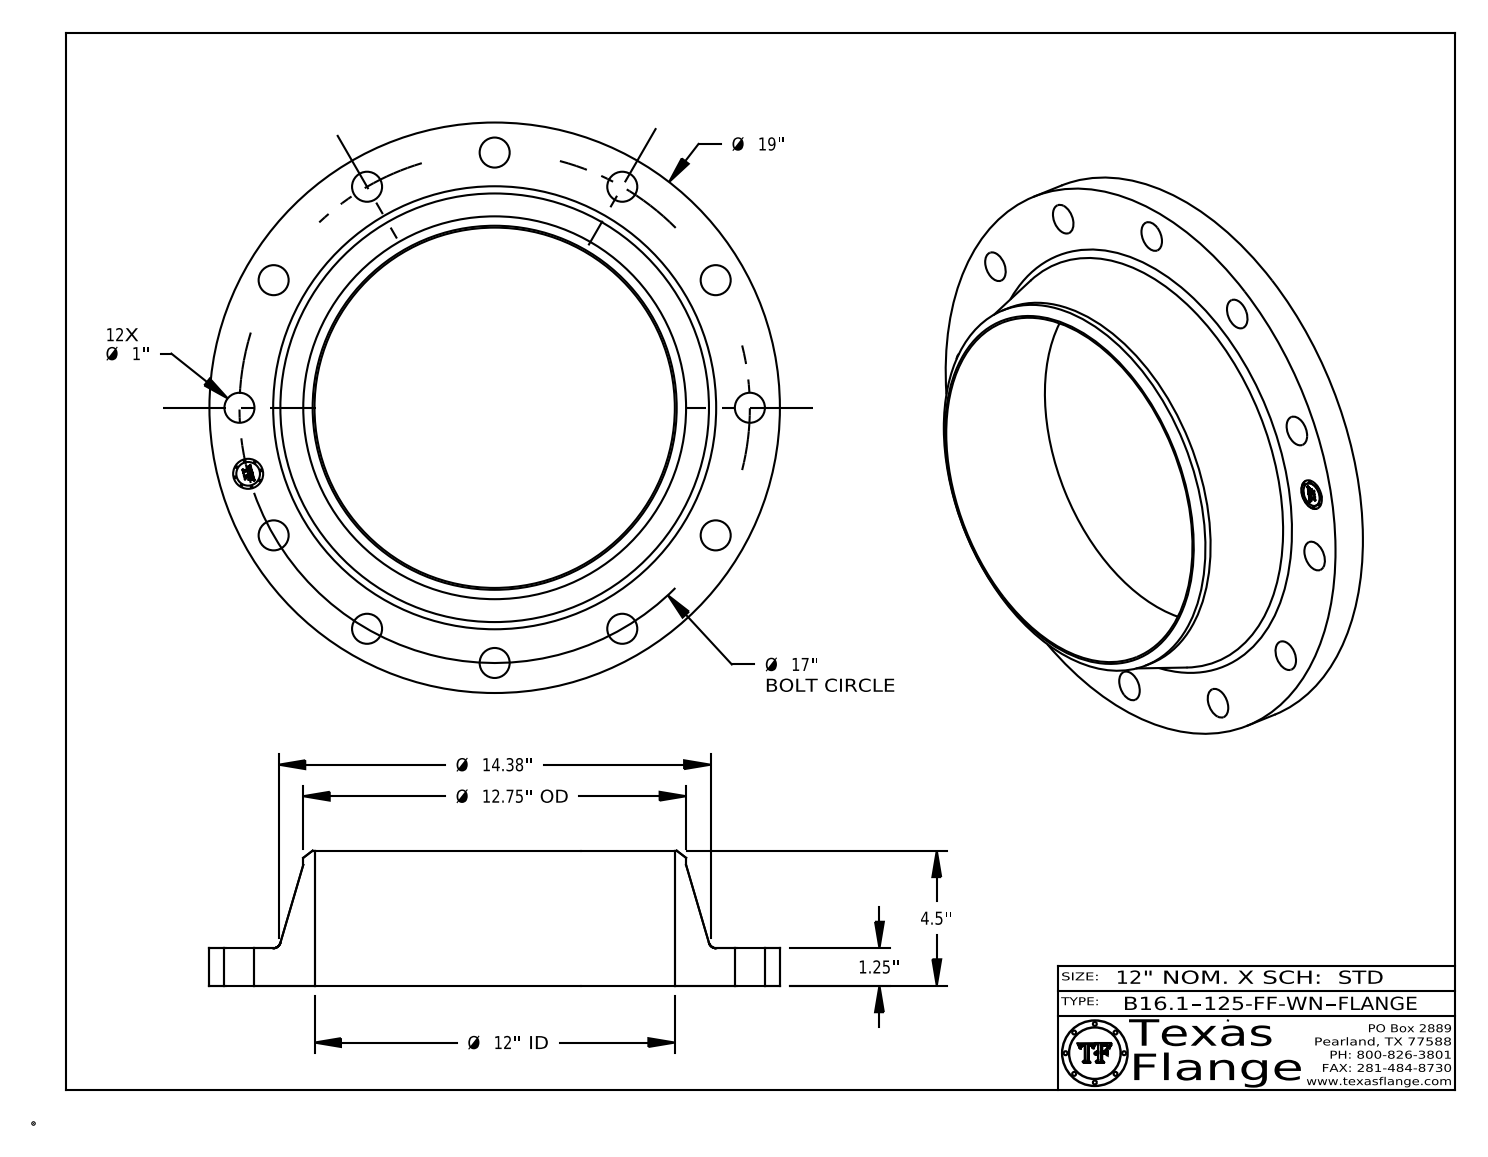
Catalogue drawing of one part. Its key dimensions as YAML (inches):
part_name: "B16.1, Class 125-FF-WN"
step_written_by: "CATIA V5 STEP AP214 (AUTOMOTIVE_DESIGN)"
units: inches
bodies: {solids: 1, faces: 424, planar: 368, cylindrical: 50, other: 6}
overall_size: [19, 19, 4.5]
volume: 294.7
surface_area: 712.3
round_holes:
  - {diameter: 1, count: 13}
  - {diameter: 12, count: 1}
round_bosses_or_shafts:
  - {diameter: 0.061, count: 8}
  - {diameter: 19, count: 1}
  - {diameter: 12.75, count: 1}
  - {diameter: 0.788, count: 1}
face_to_face_distances: [1.25, 4.5, 3.25, 0.015, 1.235, 3.265, 0.298, 0.292, 0.054, 0.193]
hole_center_spacings: [8.5, 16.42, 4.4, 12.02, 14.722, 4.4, 12.021, 14.722]
